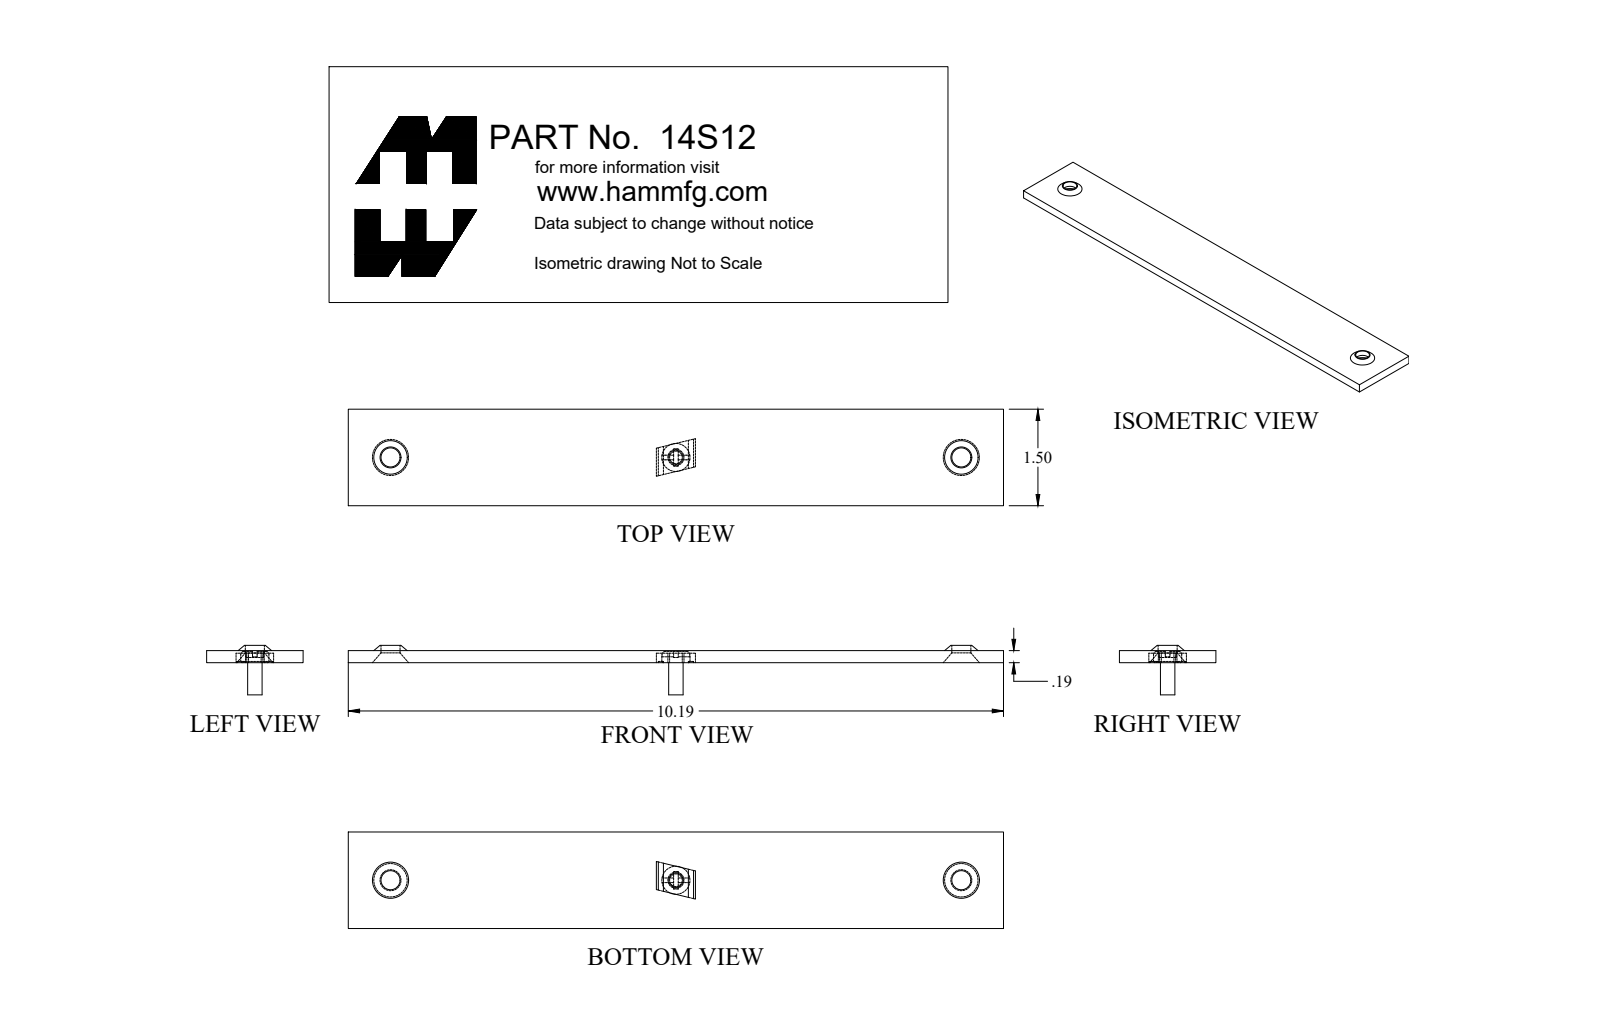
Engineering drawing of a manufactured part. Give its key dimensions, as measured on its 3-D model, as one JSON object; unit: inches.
{"part_name": "14S12", "step_written_by": "SolidWorks 2018 (AUTOMOTIVE_DESIGN)", "units": "inches", "bodies": {"solids": 1, "faces": 14, "planar": 8, "cylindrical": 2, "other": 4}, "overall_size": [10.187, 1.5, 0.27], "volume_in3": 2.834, "surface_area_in2": 35.16, "round_holes": [[0.296, 2]], "face_to_face_distances": [0.188, 1.5, 10.187, 0.27, 0.082], "hole_center_spacings": [8.875]}
